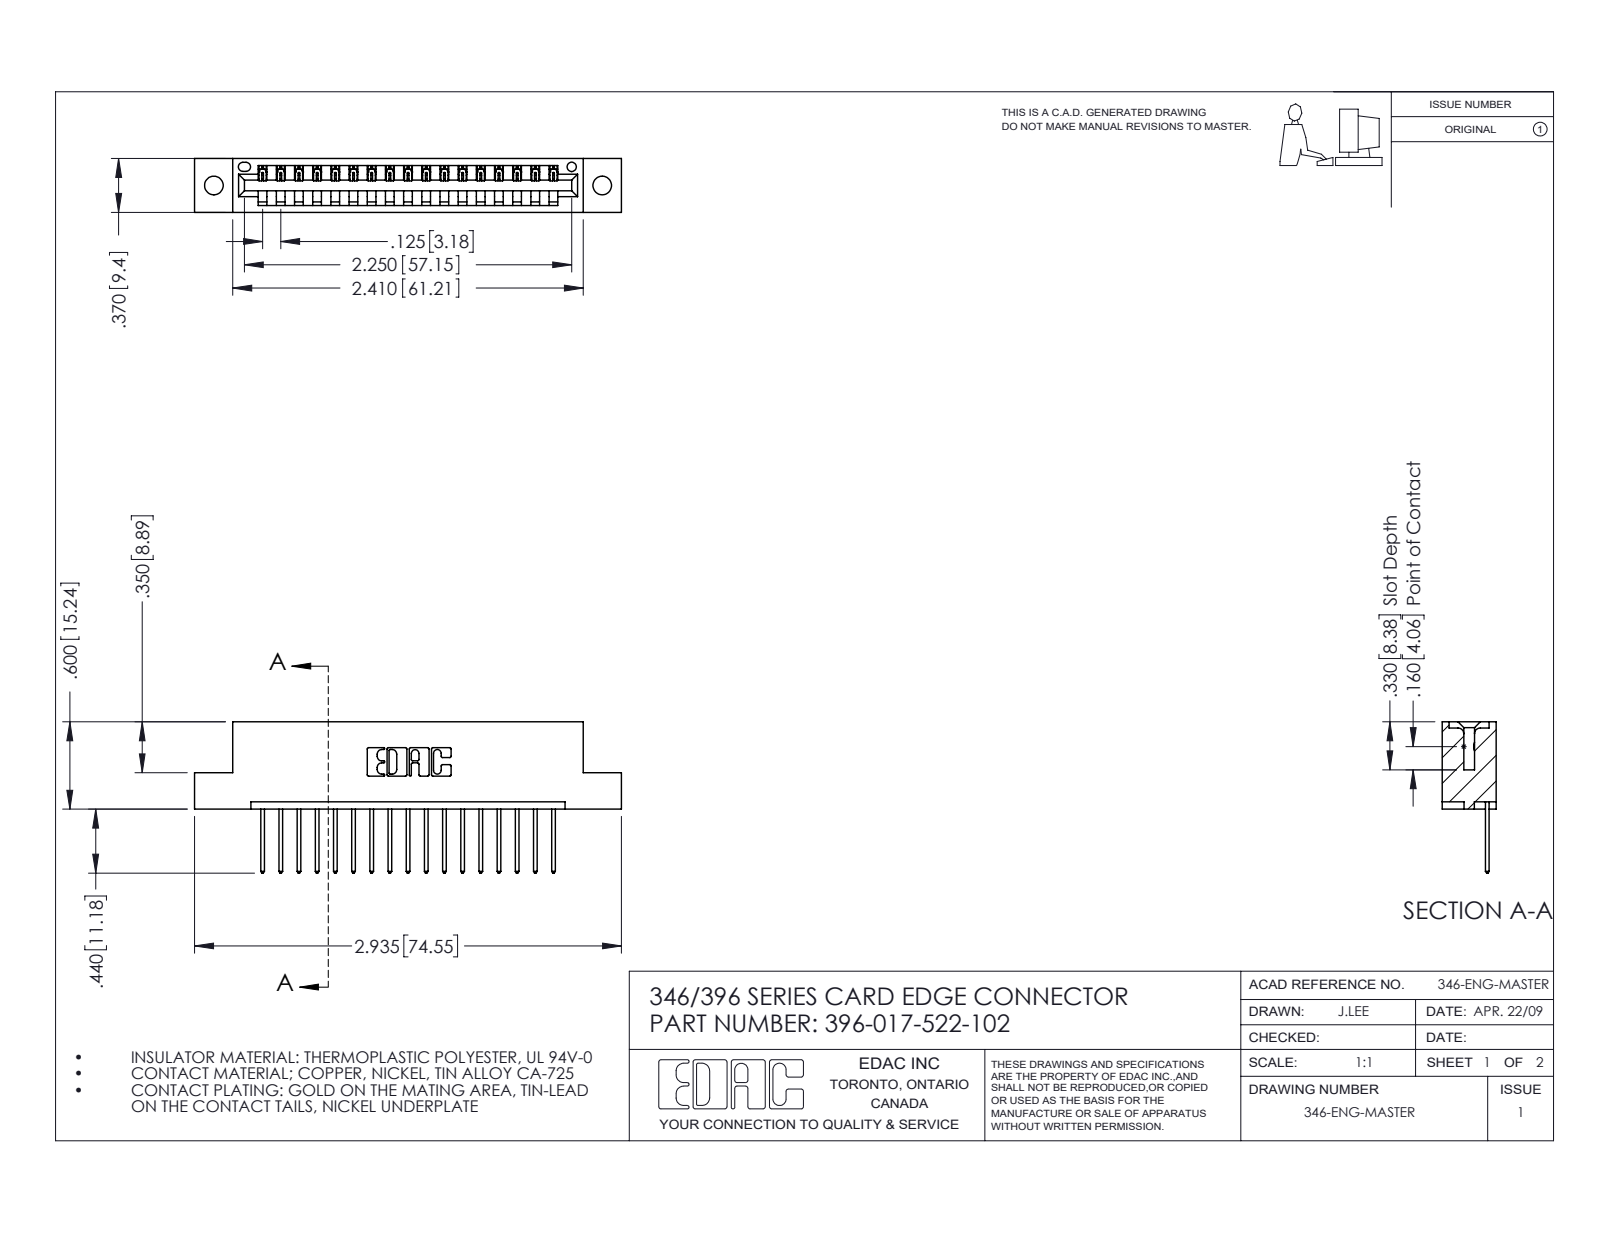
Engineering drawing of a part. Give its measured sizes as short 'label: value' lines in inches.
name: 345-292-001_345-293-122; 396-017-522-102; 346 Part_Flush Mounting Lugs - 0.128 Dia
written by: SolidWorks 2016 (CONFIG_CONTROL_DESIGN)
unit: in
bodies: 18 solids, 1108 faces (756 planar, 352 cylindrical, 0 other)
size: 2.935 × 1.04 × 0.37
volume: 0.423 in³; area: 12.68 in²
holes: 2× ⌀0.128, 1× ⌀0.064
rounds: 34× R0.006, 34× R0.01, 22× R0.01, 6× R0.007, 6× R0.031, 3× R0.026, 2× R0.031, 2× R0.04
face distances: 0.048, 0.322, 0.25, 0.37, 0.072, 0.298, 0.025, 0.148, 0.222, 0.1
hole spacings: 0.246, 2.463, 2.67
